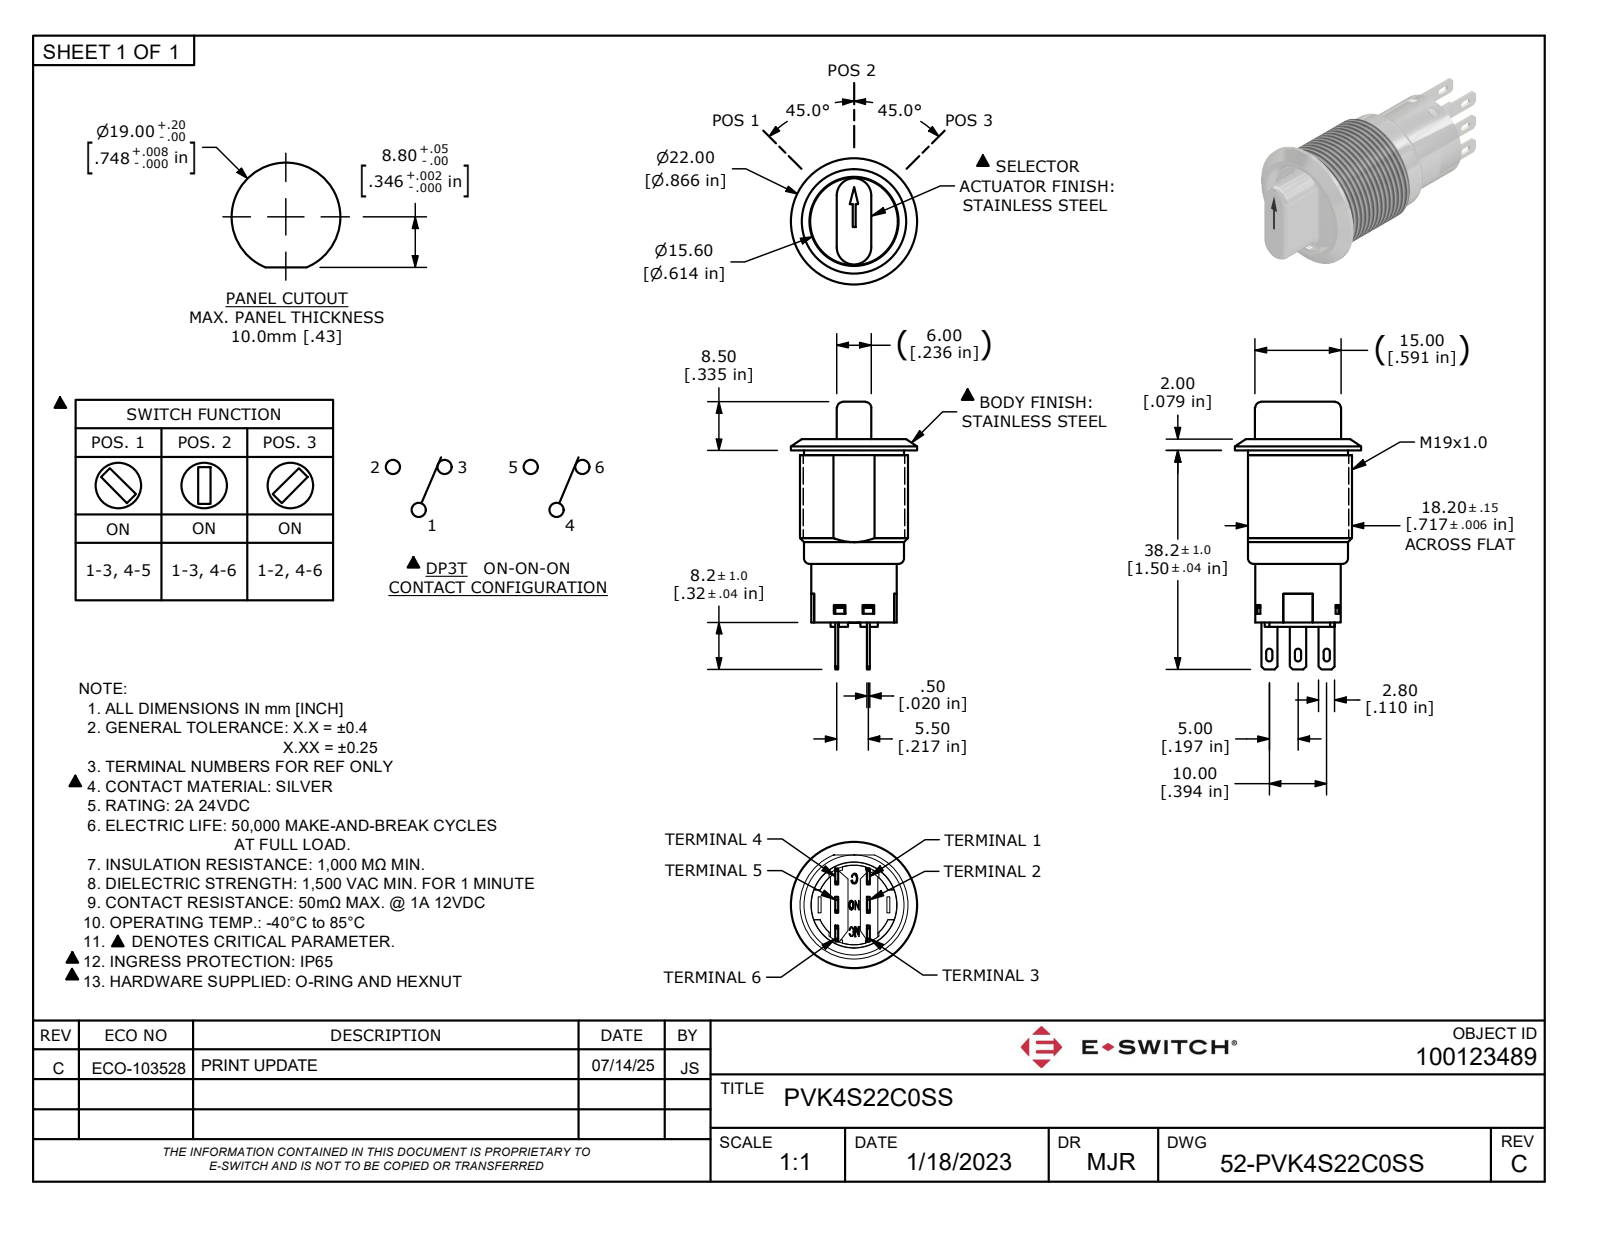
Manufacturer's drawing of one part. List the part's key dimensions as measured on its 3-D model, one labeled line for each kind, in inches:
Part name (STEP PRODUCT): PVK4S22C0SS
STEP written by: Autodesk Inventor 2022 (AUTOMOTIVE_DESIGN)
Units: inches
Bodies: 2 solids, 258 faces (169 planar, 45 cylindrical, 44 other)
Overall size (bounding box): 1.87 × 0.866 × 0.866
Volume: 0.321 in³ · Surface area: 6.936 in²
Round holes (diameter × count): ⌀0.591 ×1, ⌀0.614 ×1
Round bosses / shafts (diameter × count): ⌀0.866 ×1, ⌀0.689 ×1, ⌀0.602 ×1, ⌀0.587 ×1, ⌀0.571 ×1
Partial cylindrical surfaces — rounded edges, fillets, slot ends (radius × count): R0.022 ×6, R0.02 ×2, R0.039 ×2, R0.118 ×2, R0.254 ×1, R0.274 ×1, R0.372 ×1
Main face-to-face distances: 0.016, 0.031, 0.618, 0.602, 1.213, 1.181, 0.236, 0.02, 0.217, 0.226
